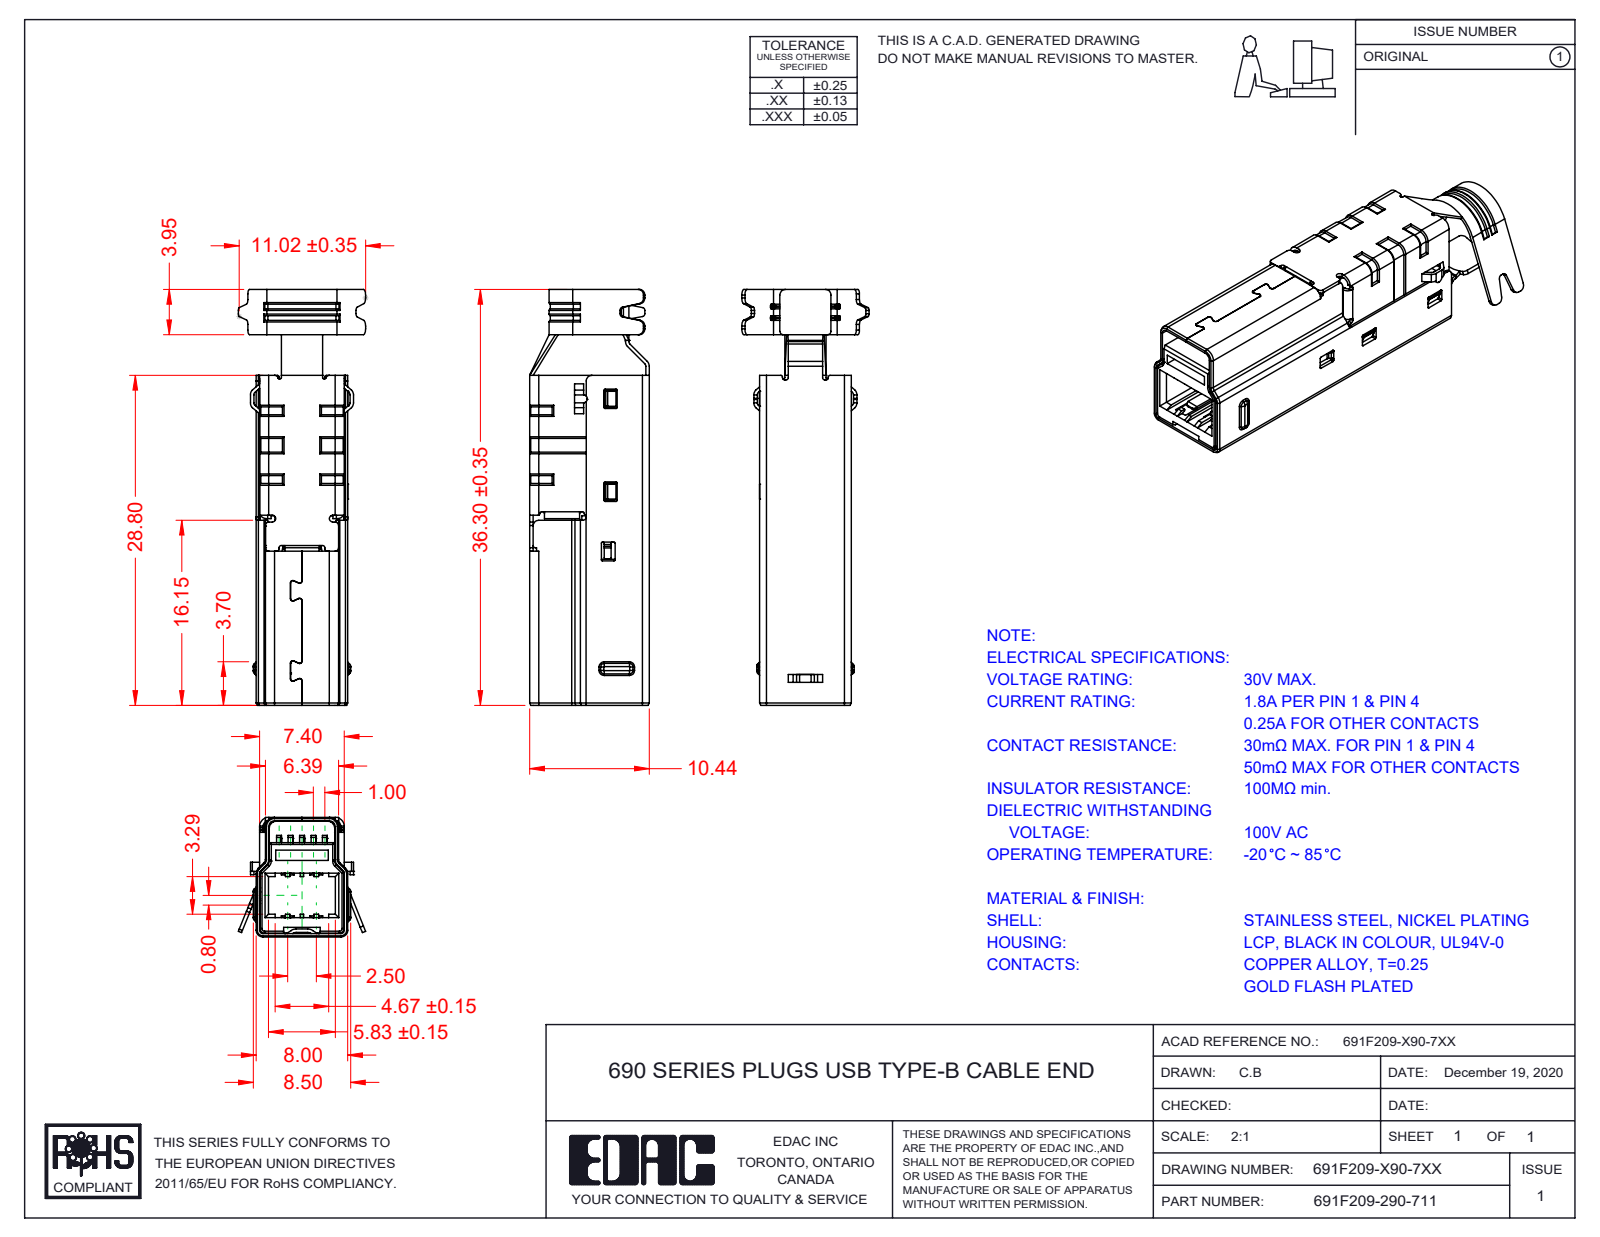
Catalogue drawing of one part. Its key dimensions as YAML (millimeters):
part_name: "Contacts 691F209-X90-7XX; 691F209-190-711; Shell 1 691F209-X90-7XX; Shell 2 691F209-X90-7XX (+1 more)"
step_written_by: "SolidWorks 2020 (AUTOMOTIVE_DESIGN)"
units: millimeters
bodies: {solids: 11, faces: 1480, planar: 816, cylindrical: 525, other: 139}
overall_size: [36.3, 11.11, 10.44]
volume: 809
surface_area: 3750
partial_cylinders:
  - {radius: 0.15, count: 130}
  - {radius: 0.1, count: 56}
  - {radius: 0.3, count: 44}
  - {radius: 0.2, count: 29}
  - {radius: 0.5, count: 22}
  - {radius: 0.6, count: 12}
  - {radius: 0.4, count: 10}
  - {radius: 0.2, count: 8}
face_to_face_distances: [7.4, 10.14, 7.7, 0.6, 7.1, 9.84, 0.81, 10.44, 8, 0.34]
